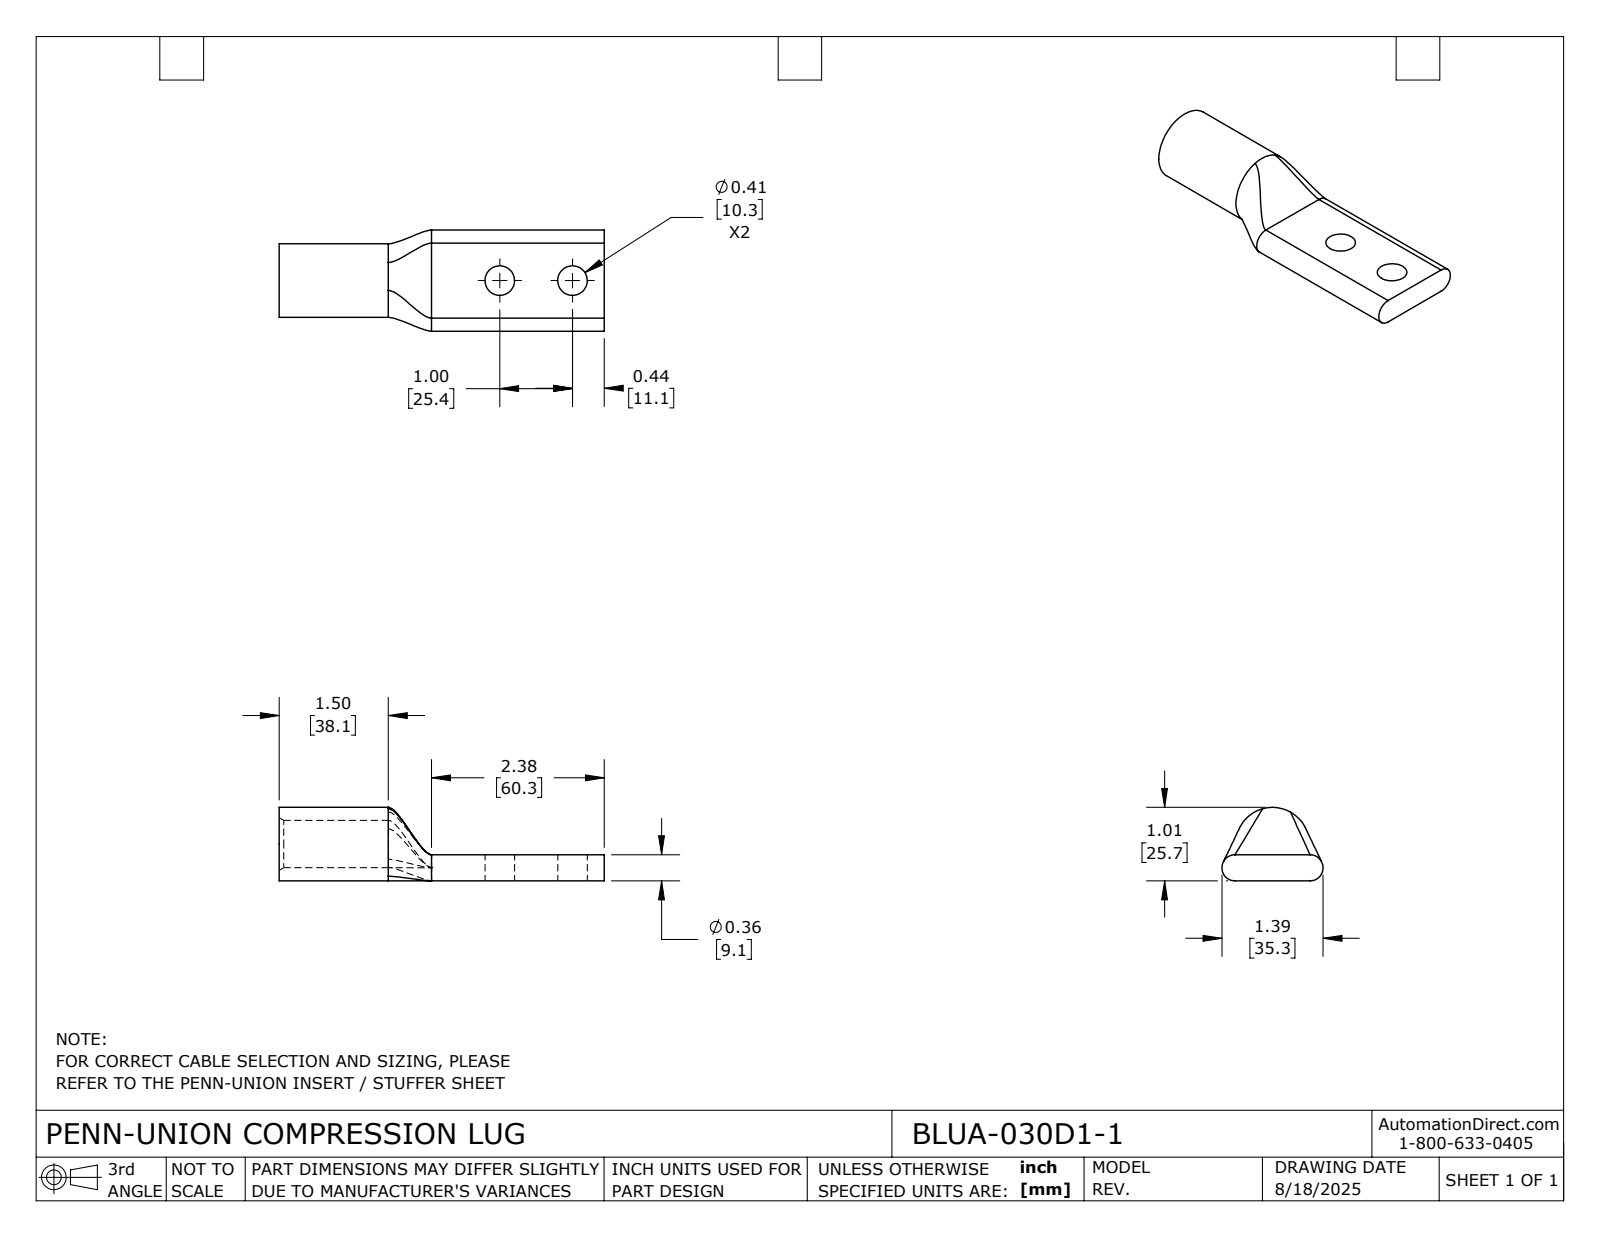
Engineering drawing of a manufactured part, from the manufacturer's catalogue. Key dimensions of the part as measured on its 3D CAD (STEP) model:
Part name (STEP PRODUCT): BLUA-030D1-1
STEP written by: SolidWorks 2024 (CONFIG_CONTROL_DESIGN)
Units: inches
Bodies: 1 solid, 26 faces (5 planar, 11 cylindrical, 10 other)
Overall size (bounding box): 4.469 × 1.391 × 1.01
Volume: 2.007 in³ · Surface area: 20.29 in²
Round holes (diameter × count): ⌀0.406 ×2, ⌀0.65 ×1
Round bosses / shafts (diameter × count): ⌀1.01 ×1
Partial cylindrical surfaces — rounded edges, fillets, slot ends (radius × count): R0.18 ×2
Main face-to-face distances: 0.359, 4.469, 2.094, 2.375
Hole centre spacings: 1
